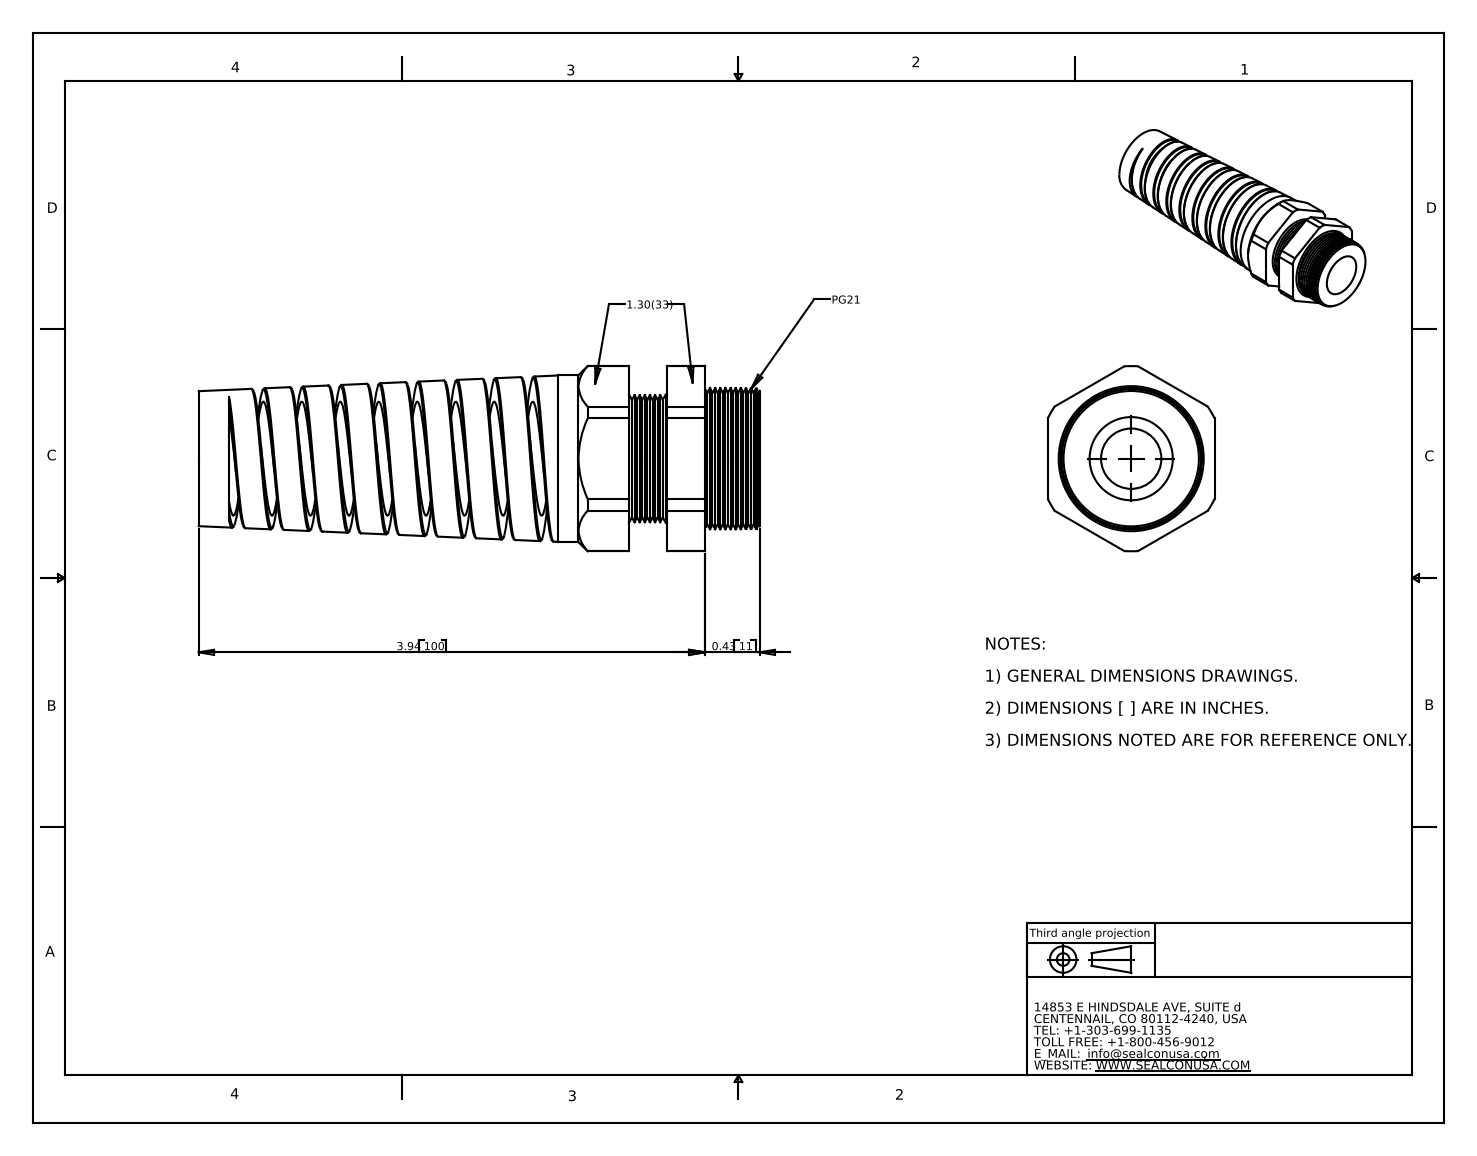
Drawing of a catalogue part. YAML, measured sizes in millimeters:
part_name: "CF21BR-GY"
step_written_by: "SolidWorks 2007 (CONFIG_CONTROL_DESIGN)"
units: millimeters
bodies: {solids: 2, faces: 188, planar: 24, cylindrical: 43, other: 121}
overall_size: [111, 36.7, 33]
volume: 39250
surface_area: 25440
round_holes:
  - {diameter: 11.9, count: 1}
  - {diameter: 22.6, count: 1}
round_bosses_or_shafts:
  - {diameter: 33, count: 1}
  - {diameter: 25.4, count: 1}
partial_cylinders:
  - {radius: 11.5, count: 1}
  - {radius: 18.3, count: 1}
face_to_face_distances: [33, 7.4, 25.9, 18.4, 14.9, 7.5, 10.9, 12.2, 19.7, 27.2]
